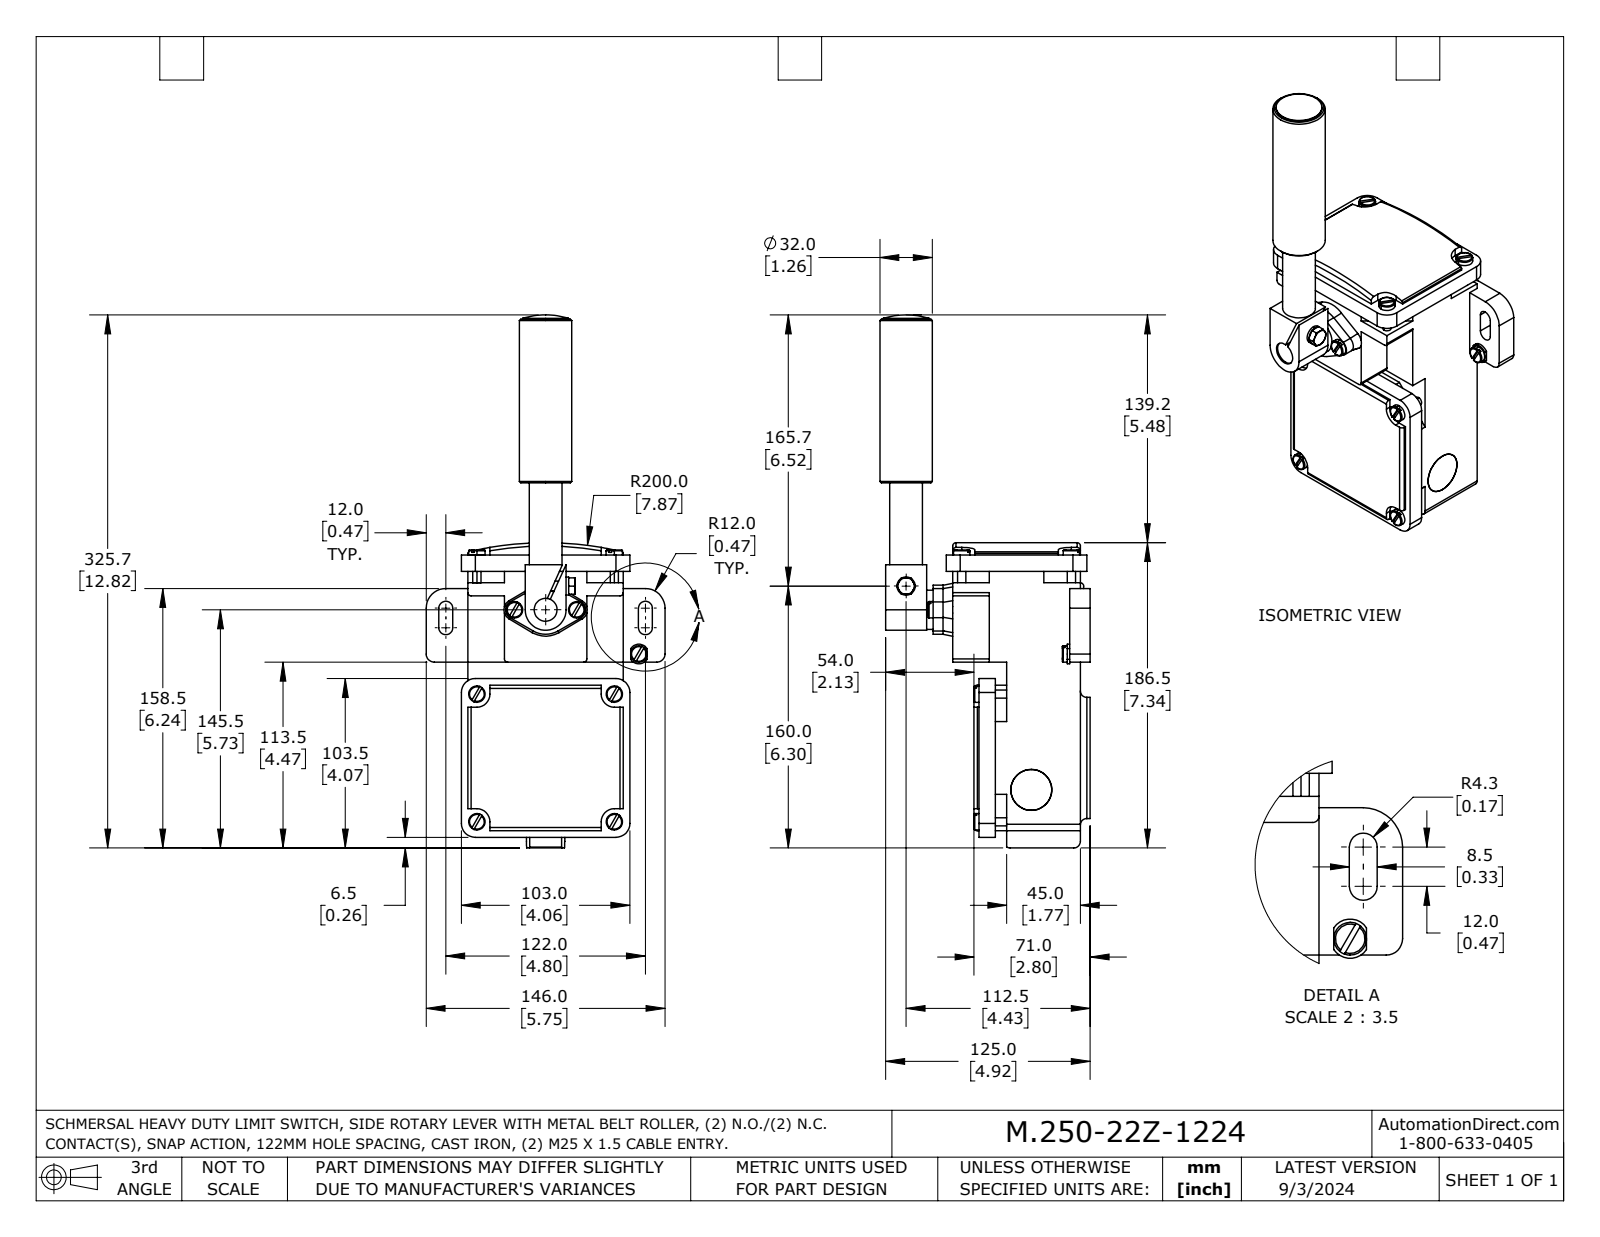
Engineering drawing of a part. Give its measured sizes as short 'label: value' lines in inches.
name: M.250-22Z-1224
written by: SolidWorks 2023 (AUTOMOTIVE_DESIGN)
unit: in
bodies: 4 solids, 372 faces (203 planar, 115 cylindrical, 54 other)
size: 12.821 × 5.748 × 5.059
volume: 80.03 in³; area: 195.2 in²
holes: 1× ⌀0.262, 1× ⌀0.92
bosses: 11× ⌀0.394, 8× ⌀0.197, 1× ⌀2.913, 1× ⌀1.26, 1× ⌀1.102, 1× ⌀0.984, 1× ⌀0.945, 1× ⌀0.787
rounds: 8× R0.079, 8× R0.315, 8× R0.335, 4× R0.157, 4× R0.167, 2× R0.039, 2× R0.197, 2× R0.217
face distances: 2.559, 3.74, 0.157, 0.236, 2.795, 0.512, 0.394, 0.787, 4.055, 2.185
hole spacings: 5.753
